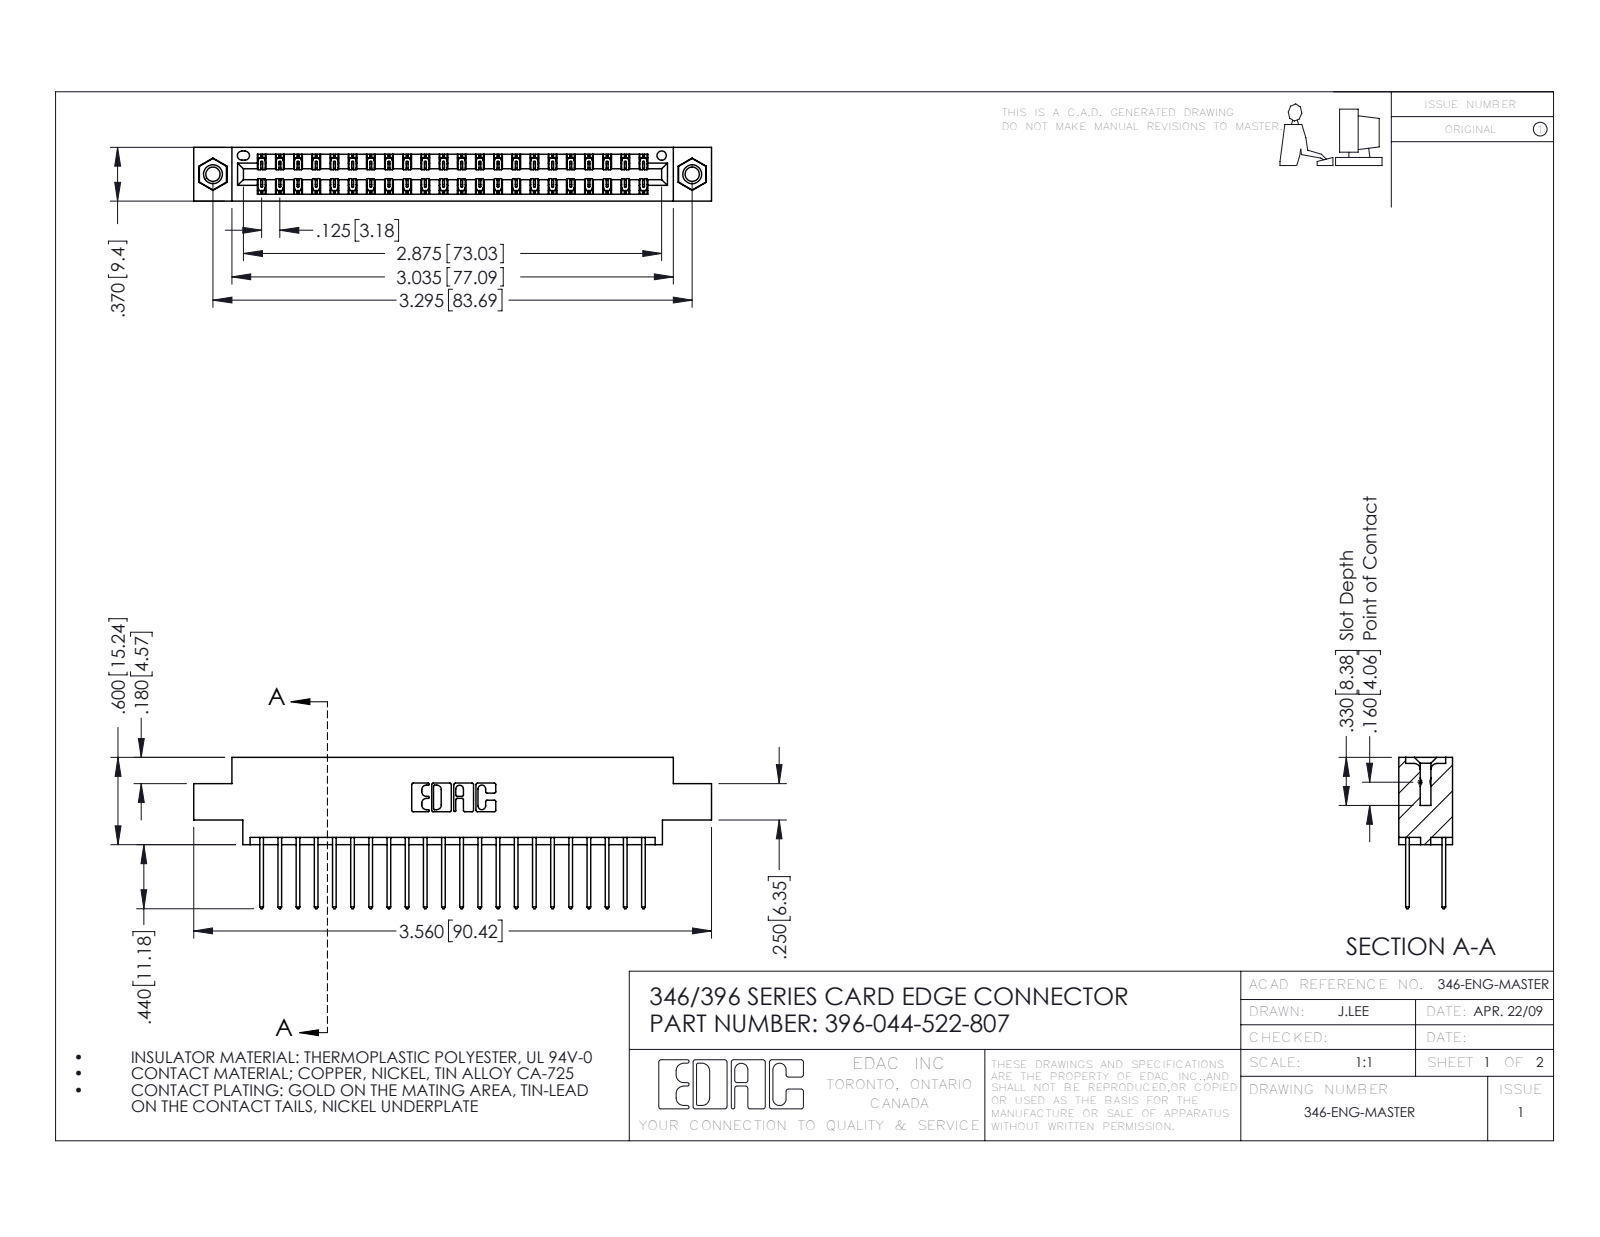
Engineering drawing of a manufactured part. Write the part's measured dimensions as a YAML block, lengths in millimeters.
part_name: "345-292-001_345-293-122; 345-250-001_345-250-005-103; 396-044-522-807; 346 Part_0.170 Offset - 0.156 Dia-TI"
step_written_by: "SolidWorks 2016 (CONFIG_CONTROL_DESIGN)"
units: millimeters
bodies: {solids: 47, faces: 2474, planar: 1652, cylindrical: 806, other: 16}
overall_size: [90.4, 26.4, 9.4]
volume: 8600
surface_area: 12250
round_holes:
  - {diameter: 2.5, count: 2}
  - {diameter: 3.2, count: 2}
  - {diameter: 4, count: 2}
  - {diameter: 1.6, count: 1}
round_bosses_or_shafts:
  - {diameter: 3.9, count: 2}
partial_cylinders:
  - {radius: 0.2, count: 66}
  - {radius: 0.3, count: 44}
  - {radius: 0.3, count: 22}
  - {radius: 0.2, count: 6}
  - {radius: 0.8, count: 6}
  - {radius: 0.7, count: 3}
  - {radius: 0.4, count: 2}
  - {radius: 0.6, count: 2}
face_to_face_distances: [1.2, 8.2, 6.4, 9.4, 1.8, 7.6, 0.6, 7, 5.6, 3.8]
hole_center_spacings: [6.2, 78.4, 83.7]
